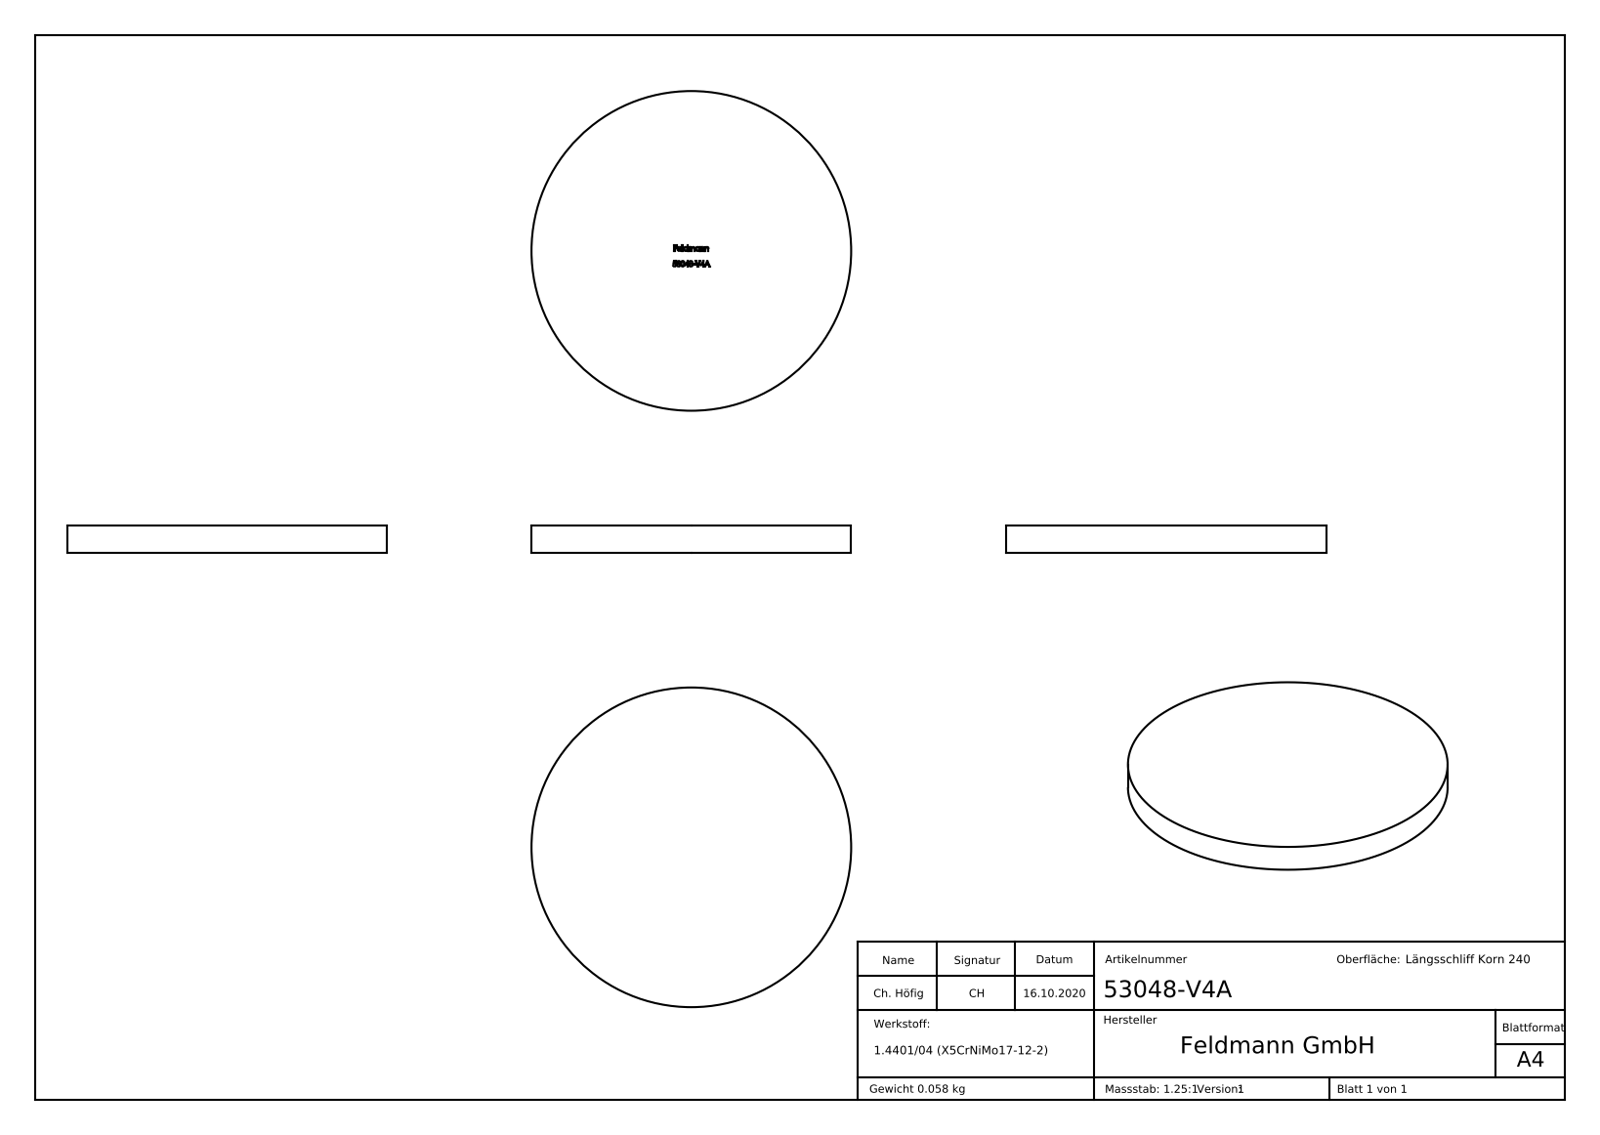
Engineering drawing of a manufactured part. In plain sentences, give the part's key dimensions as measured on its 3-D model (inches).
The part is named "53048-V4A". Its 3-D file was written by "SolidWorks 2018 (CONFIG_CONTROL_DESIGN)". It is 1 solid with 237 faces: 139 planar, 2 cylindrical and 96 other. Overall it measures 1.89 by 1.89 by 0.157 inches. Its volume is 0.442 cubic inches and its surface area 6.553 square inches. Round bosses or shafts: 1 of diameter 1.89. The main face-to-face distances are 0.157, 0.154, 0.031, 0.039, 0.079, 0.07, 0.096, 0.076, 0.033, 0.017.
